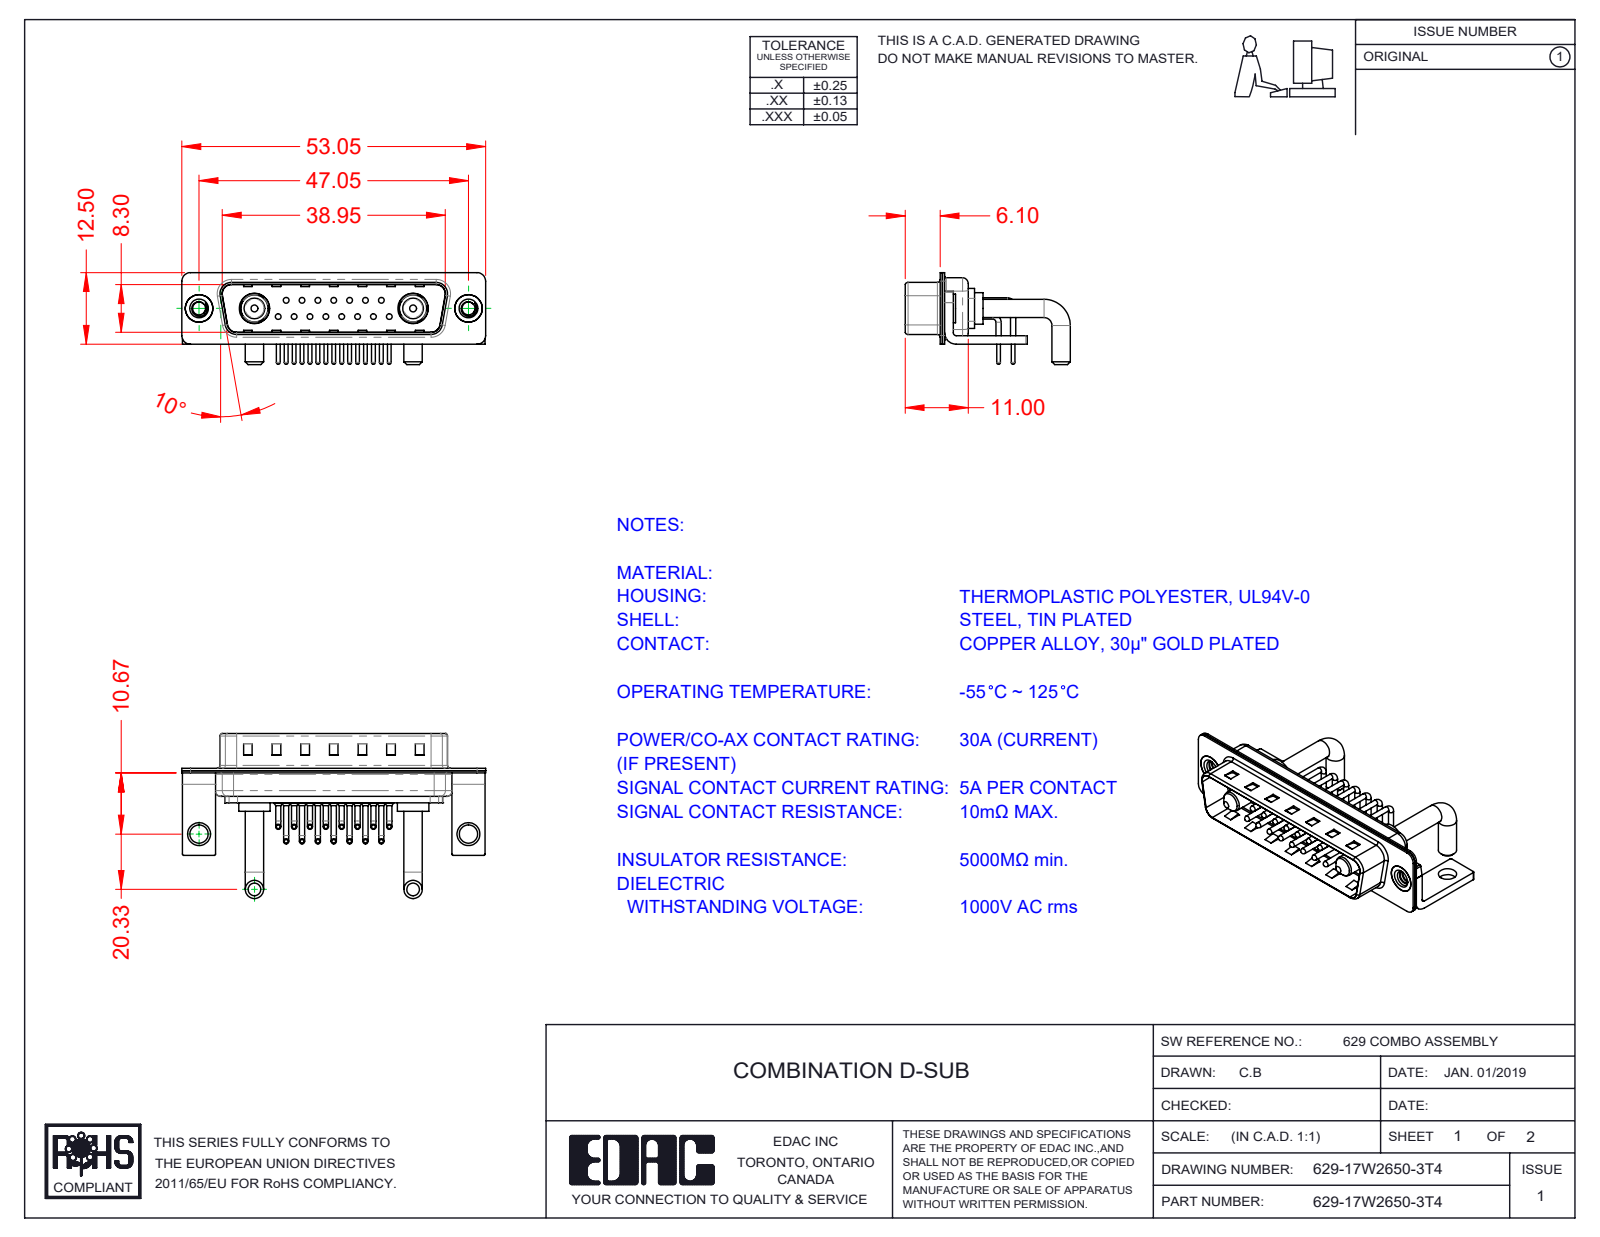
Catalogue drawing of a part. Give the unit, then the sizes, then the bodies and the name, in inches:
Units: inches
Overall size (bounding box): 2.089 × 1.135 × 0.632
Round holes (diameter × count): ⌀0.03 ×15, ⌀0.063 ×15, ⌀0.079 ×15, ⌀0.089 ×2, ⌀0.126 ×2, ⌀0.157 ×2, ⌀0.189 ×2, ⌀0.191 ×2, ⌀0.209 ×2
Round bosses / shafts (diameter × count): ⌀0.035 ×30, ⌀0.059 ×15, ⌀0.039 ×15, ⌀0.026 ×15, ⌀0.126 ×4, ⌀0.217 ×2, ⌀0.205 ×2, ⌀0.197 ×2
Partial cylindrical surfaces — rounded edges, fillets, slot ends (radius × count): R0.01 ×16, R0.059 ×16, R0.04 ×15, R0.079 ×13, R0.02 ×9, R0.063 ×8, R0.024 ×4, R0.026 ×4
Main face-to-face distances: 0.016, 0.031, 0.374, 0.059, 0.358, 0.343, 0.39, 0.024, 0.205, 0.03
Hole centre spacings: 0.124, 0.109, 0.218, 0.327, 0.198, 0.295, 0.436, 0.198
Volume: 0.217 in³ · Surface area: 12.78 in²
Bodies: 26 solids, 2152 faces (1171 planar, 737 cylindrical, 244 other)
Part name (STEP PRODUCT): 629Combo Contact Row 2; Power Pin_Ext 30A RA; 629-17W2650-3T4; 629Combo Housing_17W2 (+5 more)
STEP written by: SolidWorks 2020 (CONFIG_CONTROL_DESIGN)
